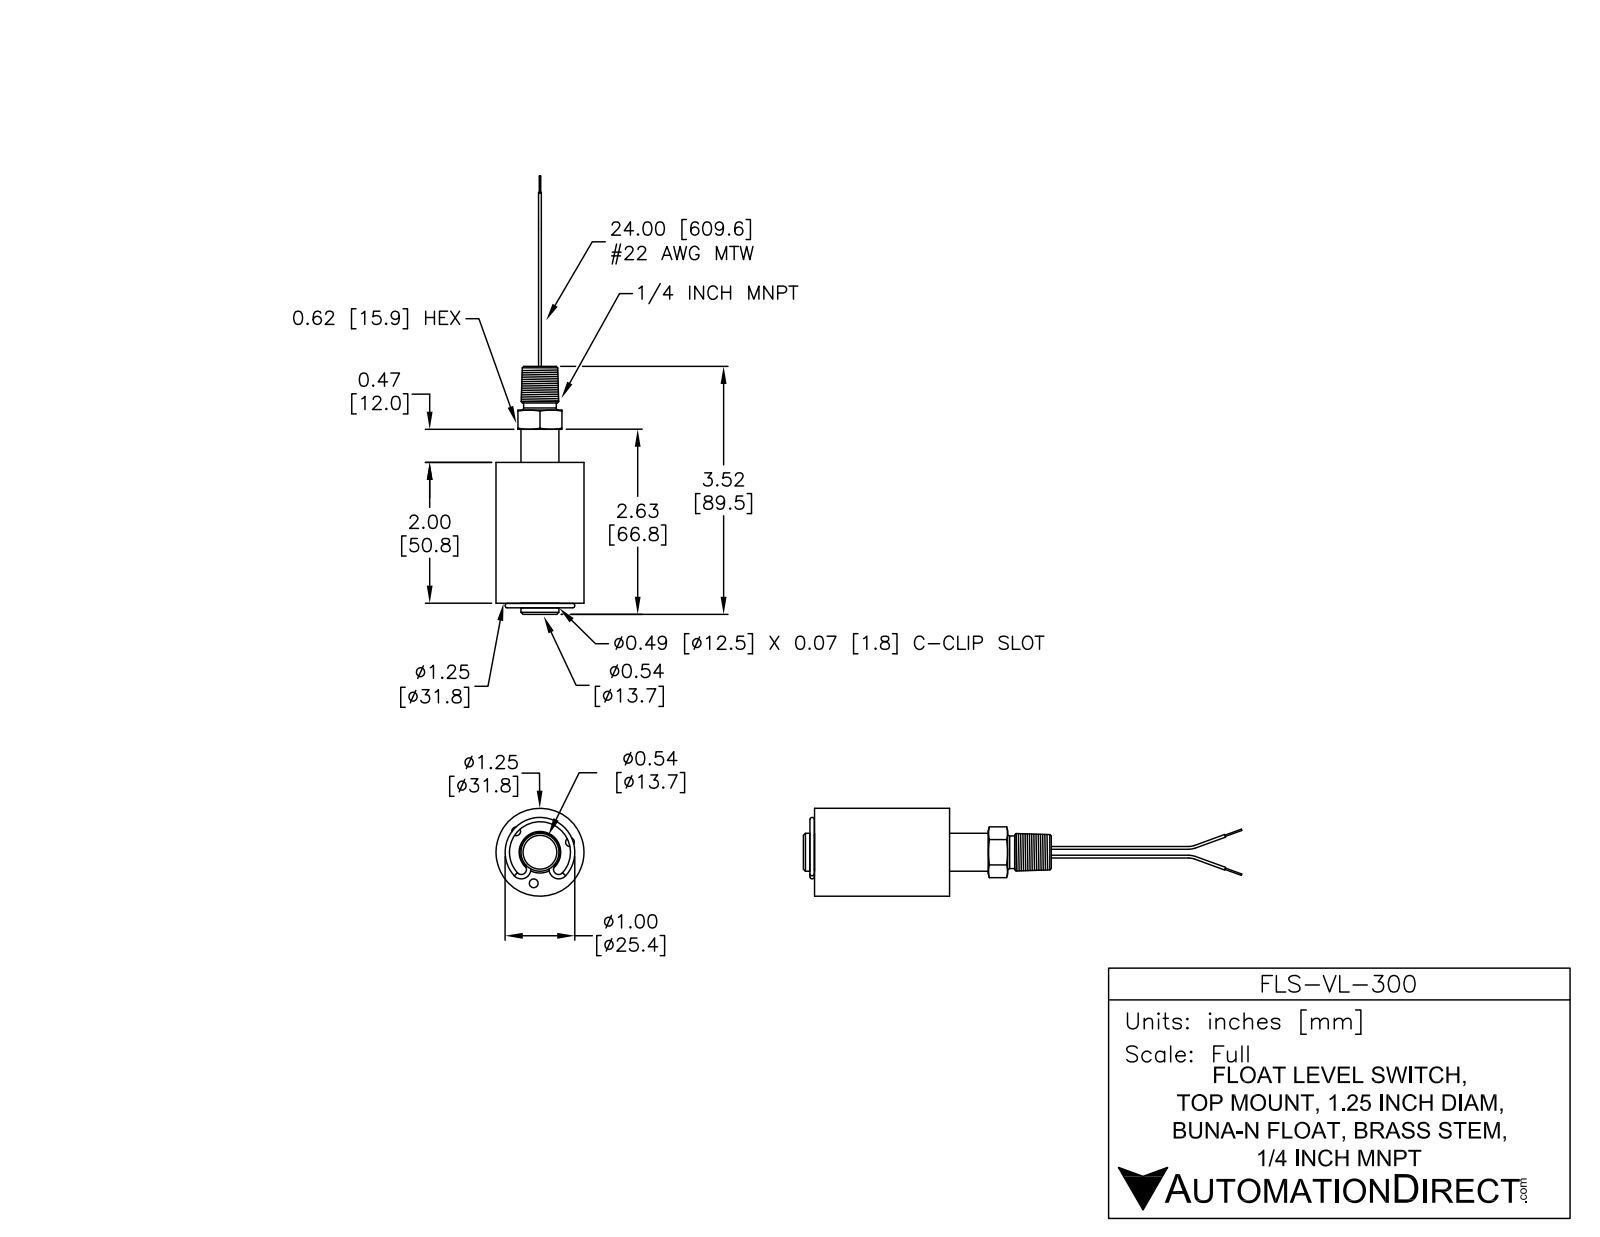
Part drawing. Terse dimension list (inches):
name: FLS-VL-300
written by: SolidWorks 2013 (AUTOMOTIVE_DESIGN)
unit: in
bodies: 6 solids, 72 faces (24 planar, 26 cylindrical, 22 other)
size: 6.229 × 1.25 × 1.25
volume: 2.381 in³; area: 26.24 in²
holes: 1× ⌀0.46, 1× ⌀0.56
bosses: 4× ⌀0.04, 2× ⌀0.02, 1× ⌀1.25, 1× ⌀0.53, 1× ⌀0.45
face distances: 2.045, 0.135, 2.18, 0.625, 2.76, 2.625, 0.58, 0.07, 0.065, 2.11
